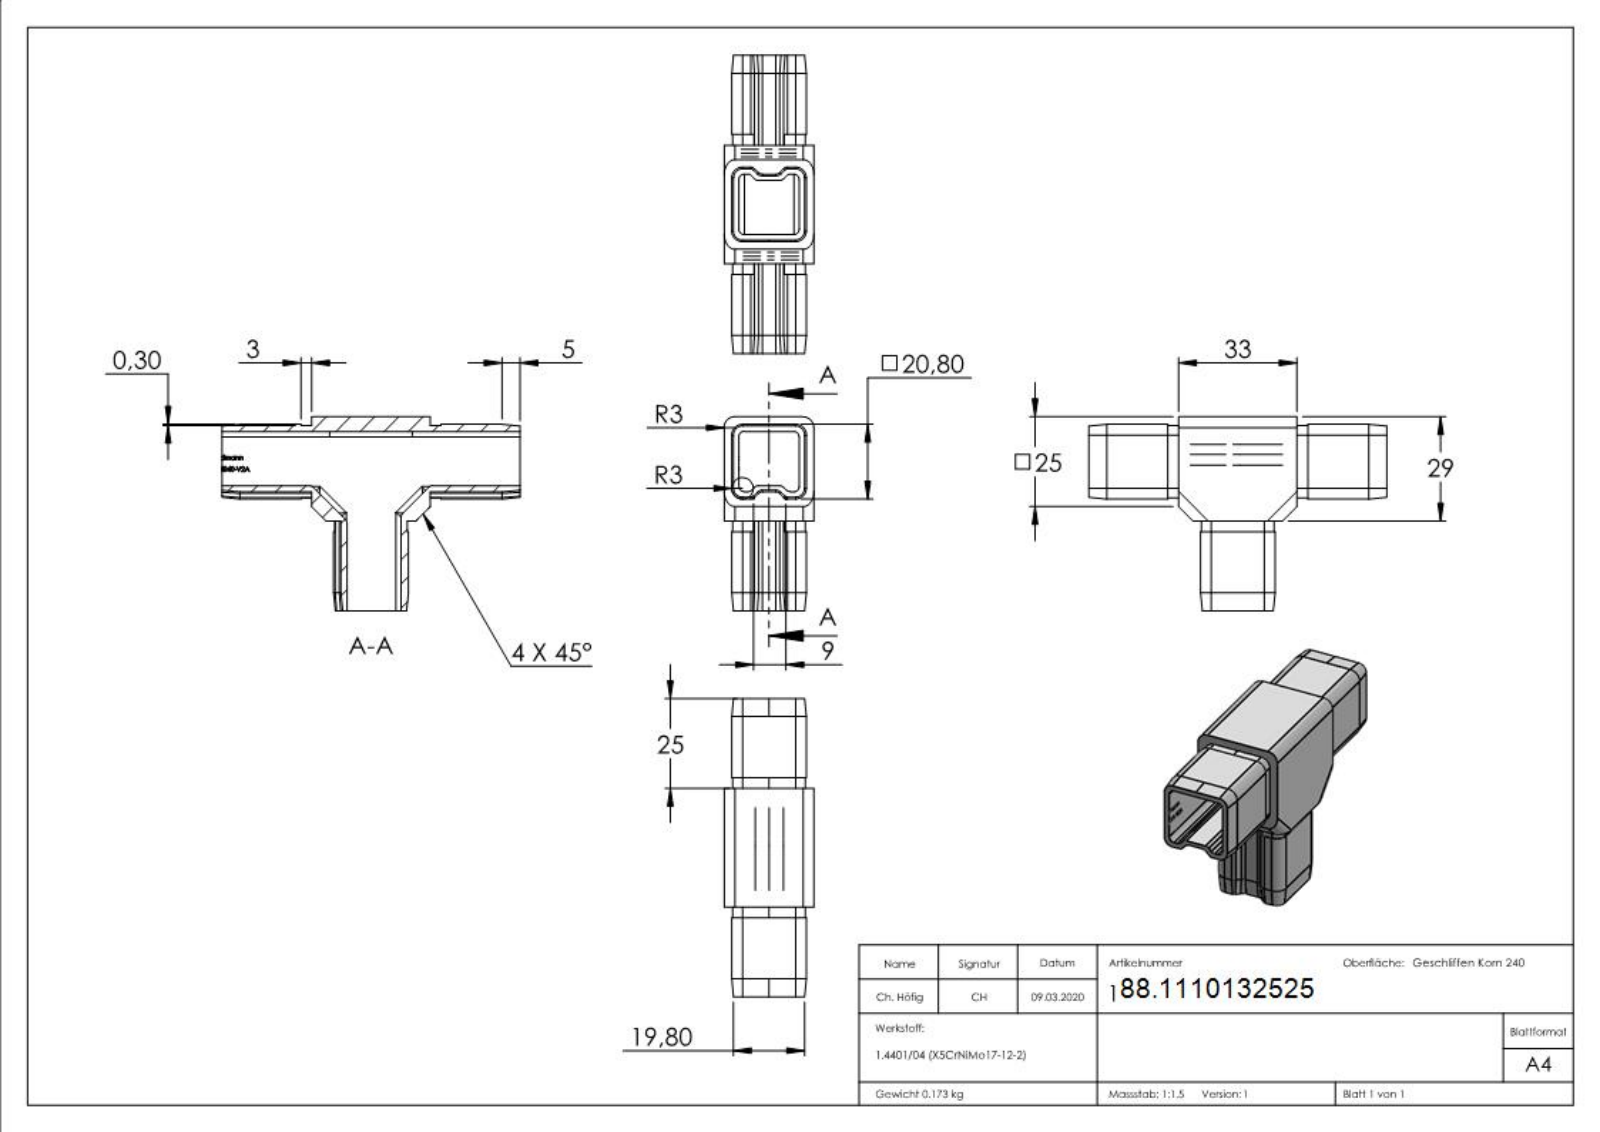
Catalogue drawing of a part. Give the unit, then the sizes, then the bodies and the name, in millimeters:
Units: millimetres
Overall size (bounding box): 83 × 54 × 25
Partial cylindrical surfaces — rounded edges, fillets, slot ends (radius × count): R1.5 ×39, R3 ×14, R2.7 ×8
Main face-to-face distances: 2, 4.1, 16.8, 18.8, 2.1, 20.9, 22.9, 25, 20.8, 1.7
Volume: 21 605 mm³ · Surface area: 17 183 mm²
Bodies: 1 solid, 471 faces (244 planar, 86 cylindrical, 141 other)
Part name (STEP PRODUCT): 10132525
STEP written by: SolidWorks 2015 (CONFIG_CONTROL_DESIGN)
